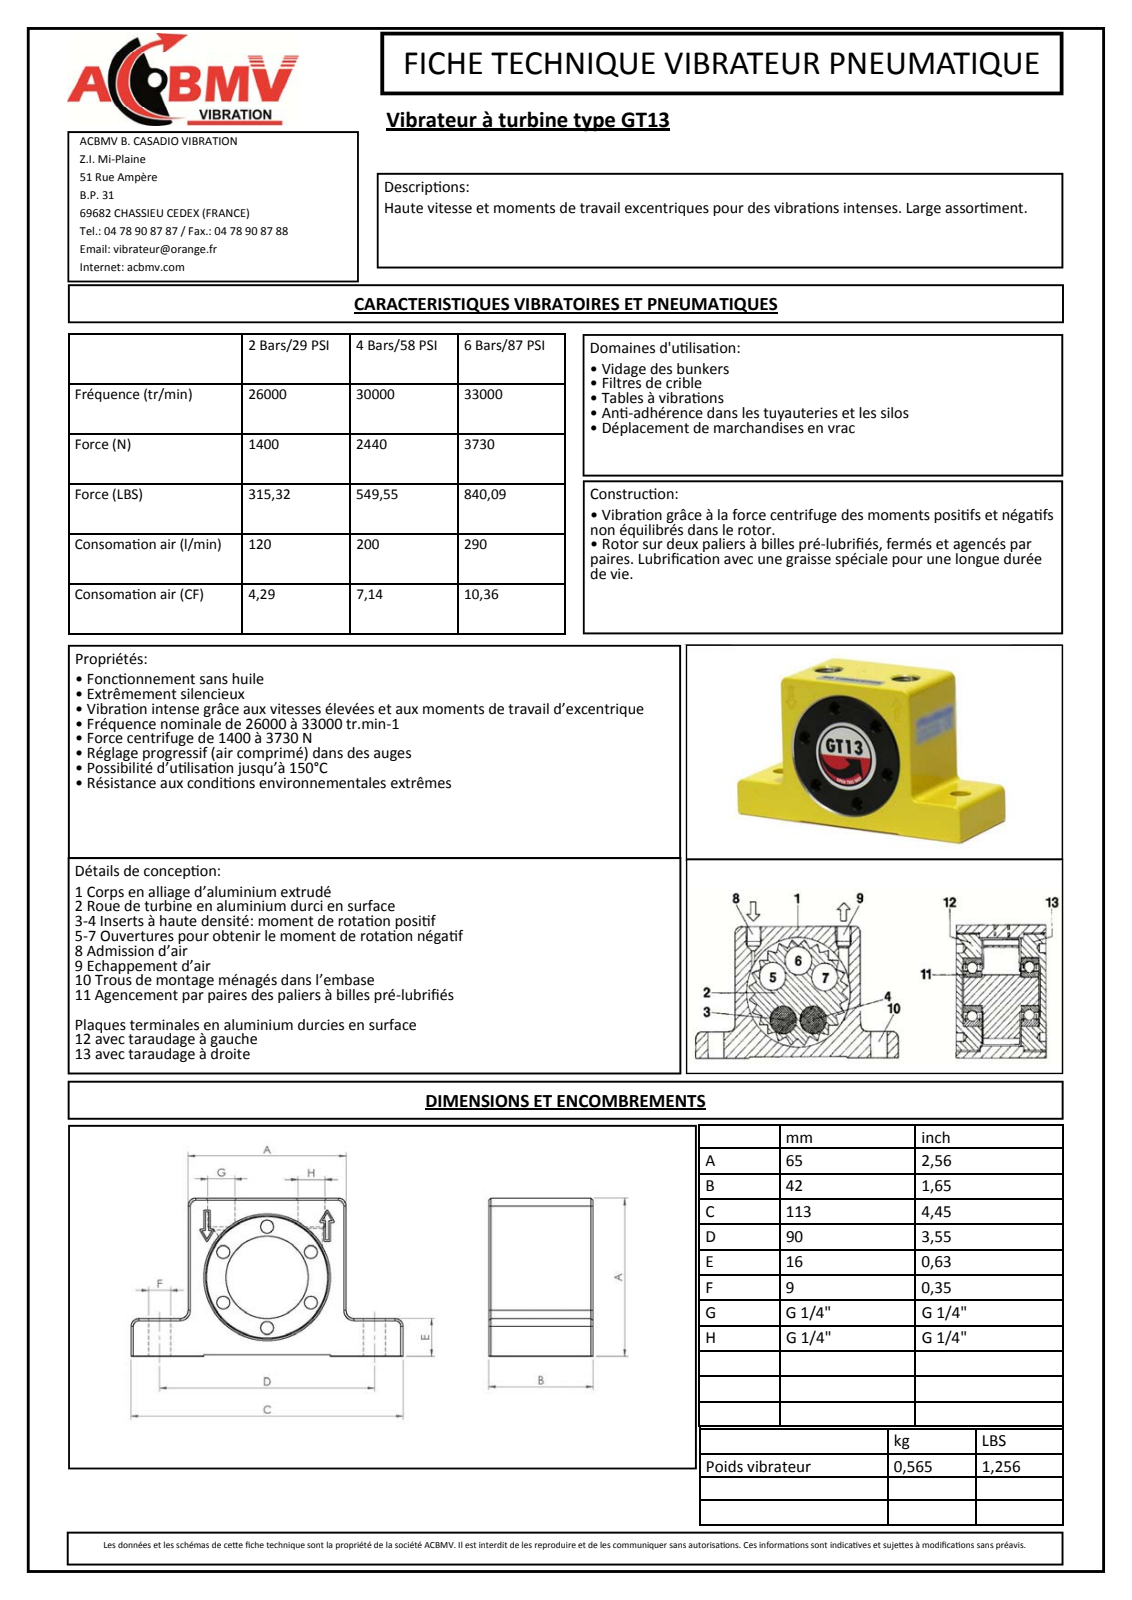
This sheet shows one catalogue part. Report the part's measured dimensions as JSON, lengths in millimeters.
{"part_name": "8013-00-M", "step_written_by": "Autodesk Inventor 2011 (CONFIG_CONTROL_DESIGN)", "units": "millimeters", "bodies": {"solids": 1, "faces": 277, "planar": 172, "cylindrical": 73, "other": 32}, "overall_size": [113, 65, 42], "volume_mm3": 195945, "surface_area_mm2": 29067, "round_holes": [[5, 6], [9, 4], [11.45, 2], [2.39, 1], [31, 1]], "round_bosses_or_shafts": [[2.15, 1]], "partial_cylinders_radius": [[0.25, 14], [2.5, 6], [0.62, 4], [0.41, 3], [0.72, 3], [0.82, 3], [1.65, 3], [0.31, 2]], "face_to_face_distances": [65, 0.5, 41.8, 42, 64.5, 0.7, 41.3, 41.1, 16, 15.5], "hole_center_spacings": [21.5, 37.24, 43, 14.26, 25.08, 34.31, 34.84, 45.45]}
